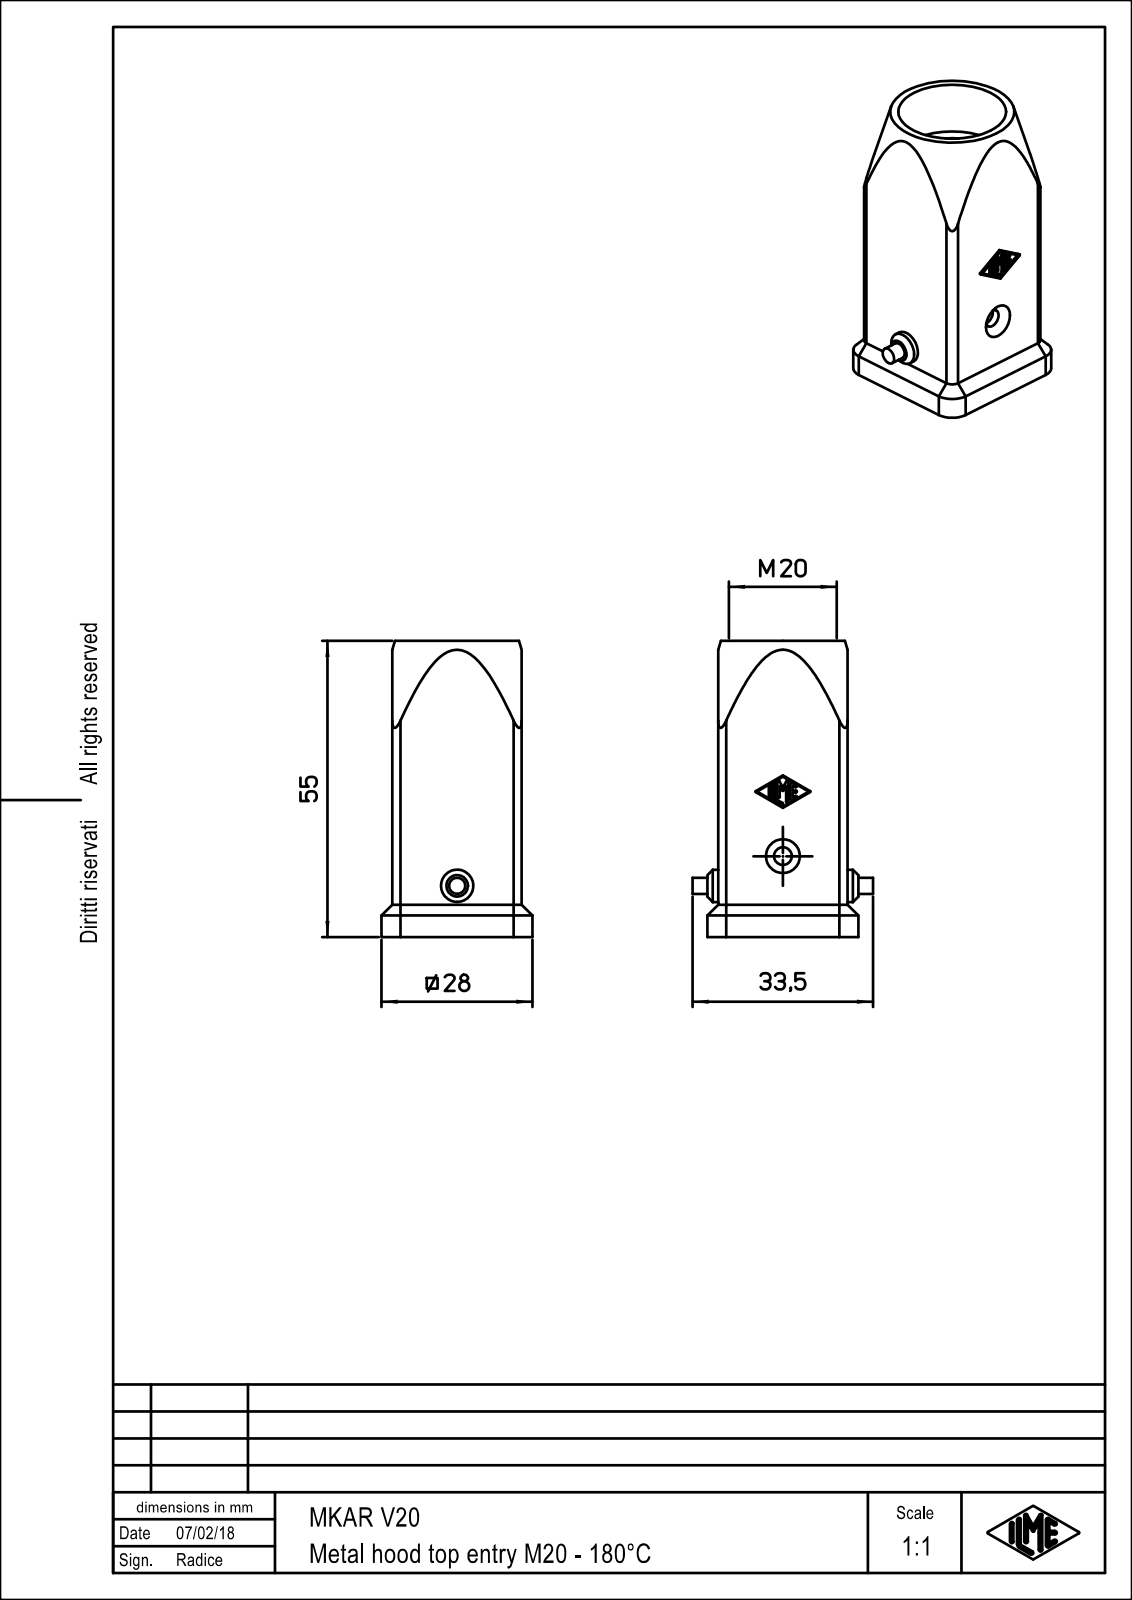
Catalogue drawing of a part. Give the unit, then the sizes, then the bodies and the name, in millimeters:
Units: millimetres
Overall size (bounding box): 55 × 33.5 × 28
Round holes (diameter × count): ⌀3.3 ×1, ⌀15 ×1, ⌀20 ×1
Round bosses / shafts (diameter × count): ⌀6 ×1, ⌀3 ×1
Partial cylindrical surfaces — rounded edges, fillets, slot ends (radius × count): R0.5 ×4, R1.5 ×4, R2 ×4, R3.5 ×4
Main face-to-face distances: 23, 1, 24, 22, 3, 1.5, 2, 25, 26, 42
Volume: 7 863 mm³ · Surface area: 10 607 mm²
Bodies: 1 solid, 81 faces (38 planar, 30 cylindrical, 13 other)
Part name (STEP PRODUCT): MKAR_V20
STEP written by: PTC Creo Elements/Direct Modeling 19.0E 27-Jun-2016 (C) Parametric Technology GmbH (AUTOMOTIVE_DESIGN)
